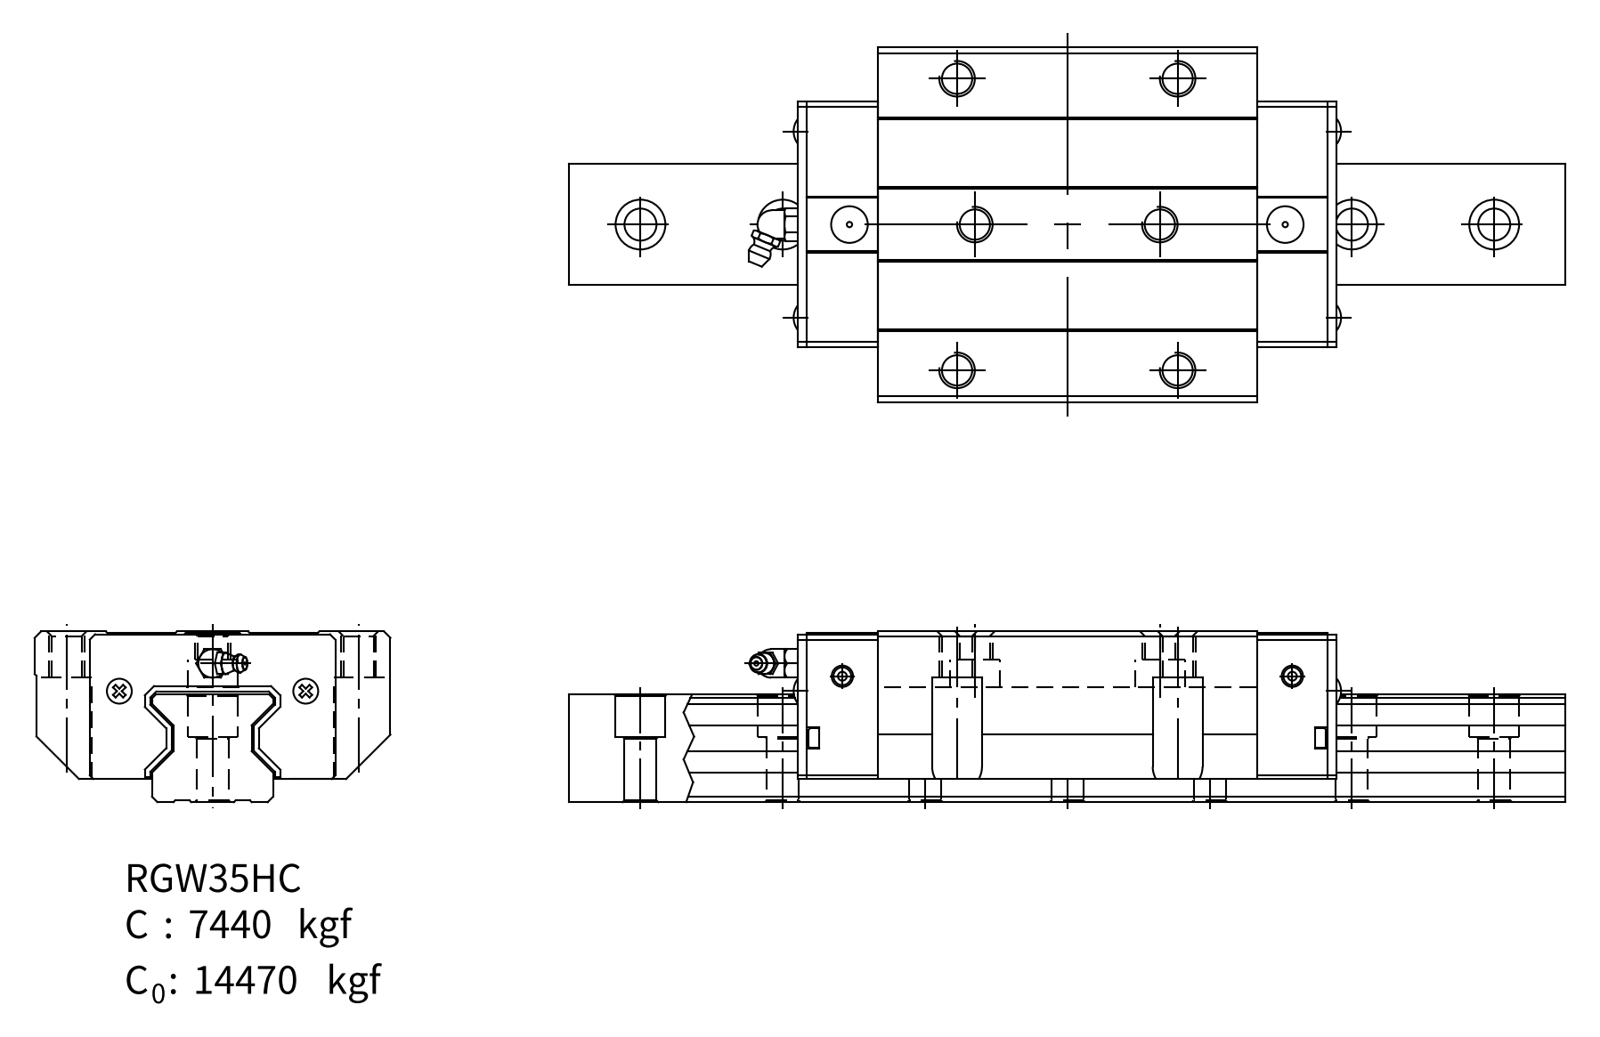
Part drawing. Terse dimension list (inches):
name: RGW35HC_BLOCK_8; PRT0010; RGW35HC_ASM_8_ASM; RGW35HC_ASM
written by: PRO/ENGINEER BY PARAMETRIC TECHNOLOGY CORPORATION, 2004360 (CONFIG_CONTROL_DESIGN)
unit: in
bodies: 2 solids, 214 faces (142 planar, 72 cylindrical, 0 other)
size: 11.811 × 3.937 × 1.89
volume: 39.56 in³; area: 166.5 in²
holes: 9× ⌀0.551, 7× ⌀0.354, 6× ⌀0.394, 3× ⌀0.406, 2× ⌀0.059, 2× ⌀0.197, 1× ⌀0.236
rounds: 4× R0.276
face distances: 0.256, 0.381, 0.02, 0.701, 1.87, 1.89, 0.933, 1.634, 1.189, 1.083
hole spacings: 1.575, 3.15, 1.626, 1.653, 2.006, 2.024, 2.515, 2.764
